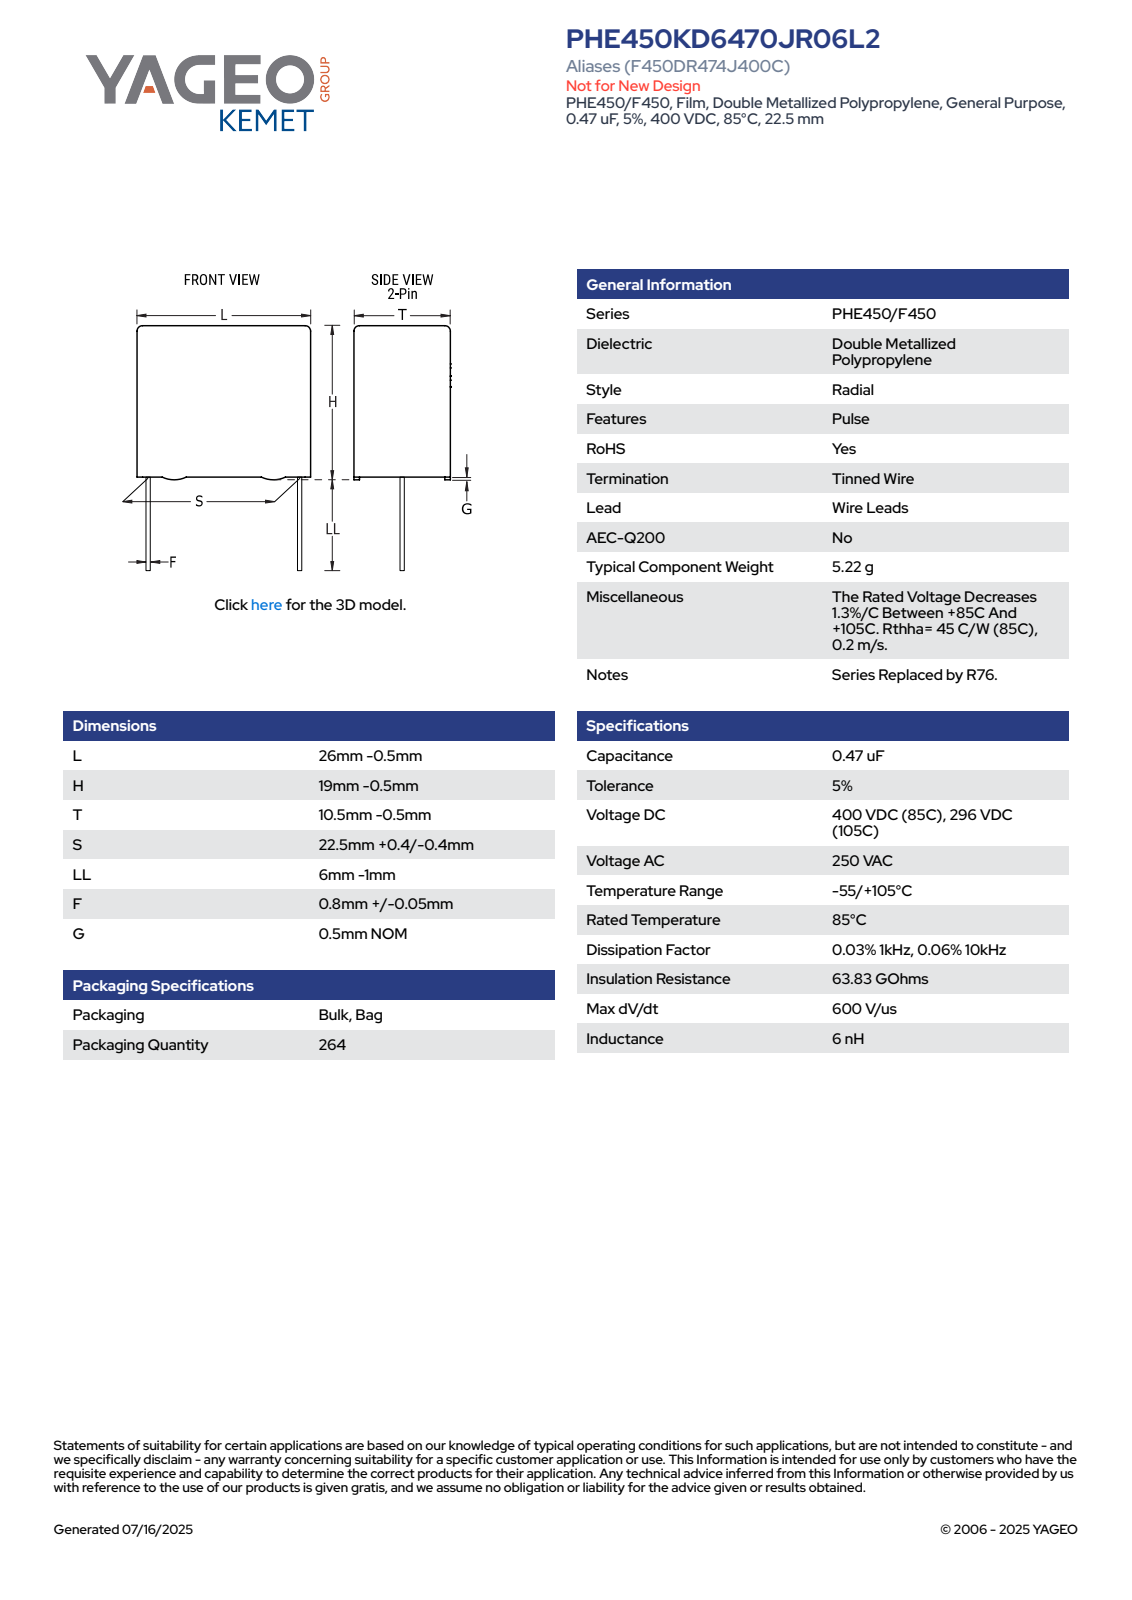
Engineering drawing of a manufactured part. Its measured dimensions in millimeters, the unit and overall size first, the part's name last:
Units: millimetres
Overall size (bounding box): 25.5 × 23.5 × 10.01
Round bosses / shafts (diameter × count): ⌀0.85 ×2
Partial cylindrical surfaces — rounded edges, fillets, slot ends (radius × count): R0.5 ×4
Main face-to-face distances: 10, 18, 25.5, 10.01, 0.5, 18.5, 0.57, 9.43, 8.86, 9.44
Volume: 4 597 mm³ · Surface area: 1 890 mm²
Bodies: 4 solids, 89 faces (81 planar, 8 cylindrical, 0 other)
Part name (STEP PRODUCT): CFR_RBG_26X19X10.5_L25.5H18.5T10S22.5LL5F0.85G0.5
STEP written by: SolidWorks 2021 (AUTOMOTIVE_DESIGN)
